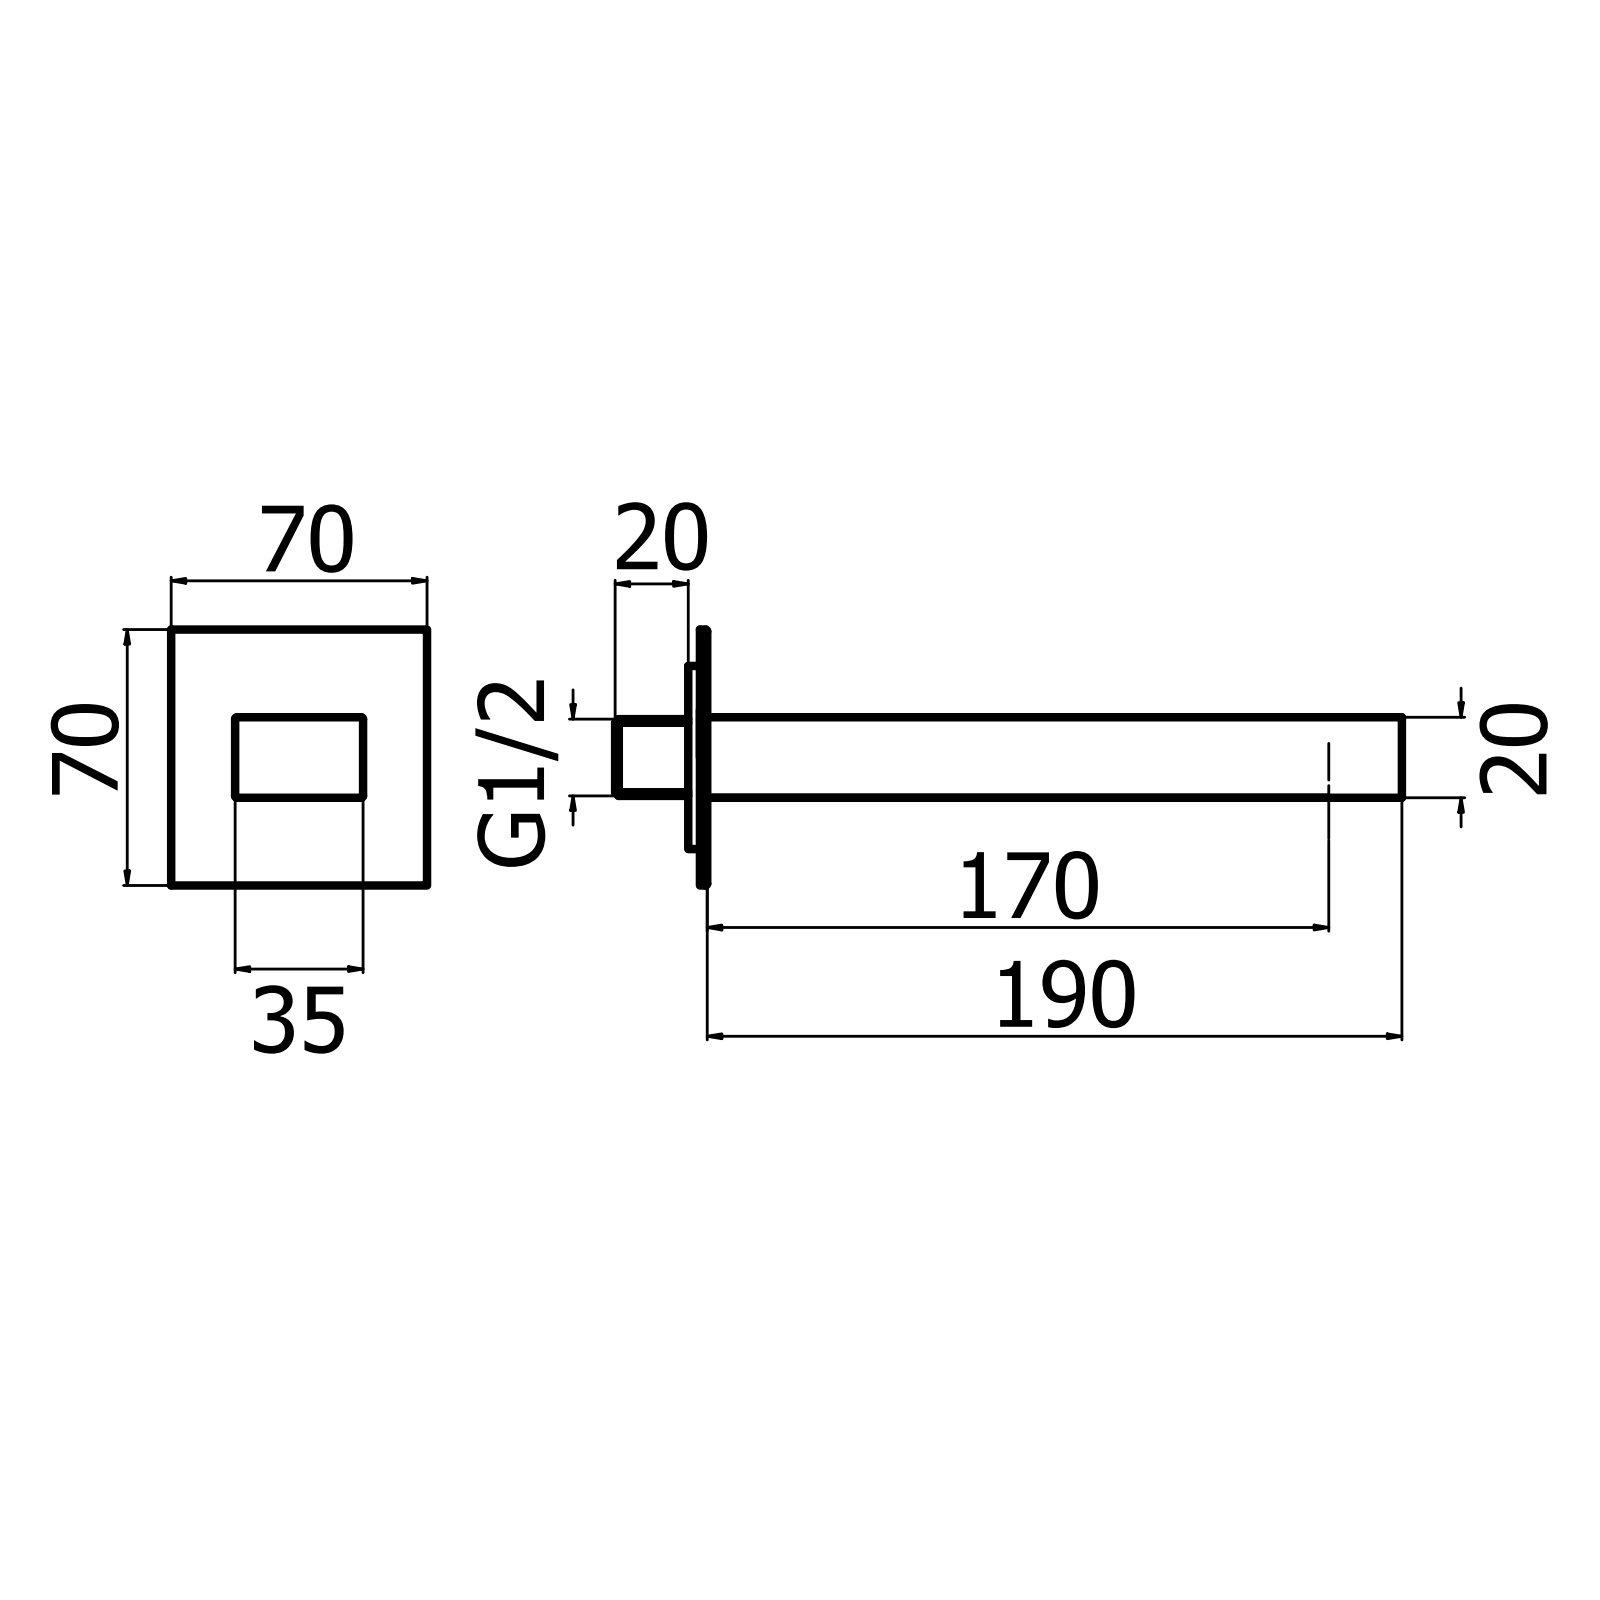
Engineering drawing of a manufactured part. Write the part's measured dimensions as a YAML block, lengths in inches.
part_name: "BOCCA_QUADRA_X_INCASSI; PIASTRA_70X70; BOCCA_QUADRA_CON_PIASTRA_QUADRA; SARMAC0014 (+4 more)"
step_written_by: "CREO PARAMETRIC BY PTC INC, 2020281 (CONFIG_CONTROL_DESIGN)"
units: inches
bodies: {solids: 5, faces: 401, planar: 286, cylindrical: 78, other: 37}
overall_size: [7.933, 2.948, 2.948]
volume: 7.176
surface_area: 80.72
round_holes:
  - {diameter: 0.163, count: 2}
  - {diameter: 0.669, count: 2}
  - {diameter: 0.039, count: 1}
  - {diameter: 0.177, count: 1}
  - {diameter: 0.276, count: 1}
  - {diameter: 0.433, count: 1}
  - {diameter: 0.591, count: 1}
  - {diameter: 0.689, count: 1}
  - {diameter: 0.74, count: 1}
  - {diameter: 0.772, count: 1}
  - {diameter: 0.795, count: 1}
  - {diameter: 0.835, count: 1}
round_bosses_or_shafts:
  - {diameter: 0.945, count: 1}
  - {diameter: 0.937, count: 1}
  - {diameter: 0.886, count: 1}
  - {diameter: 0.827, count: 1}
  - {diameter: 0.787, count: 1}
  - {diameter: 0.748, count: 1}
  - {diameter: 0.709, count: 1}
  - {diameter: 0.551, count: 1}
partial_cylinders:
  - {radius: 0.02, count: 8}
face_to_face_distances: [0.865, 0.059, 1.377, 7.874, 7.933, 0.014, 0.098, 0.024, 0.122, 0.946]
hole_center_spacings: [0.354]
